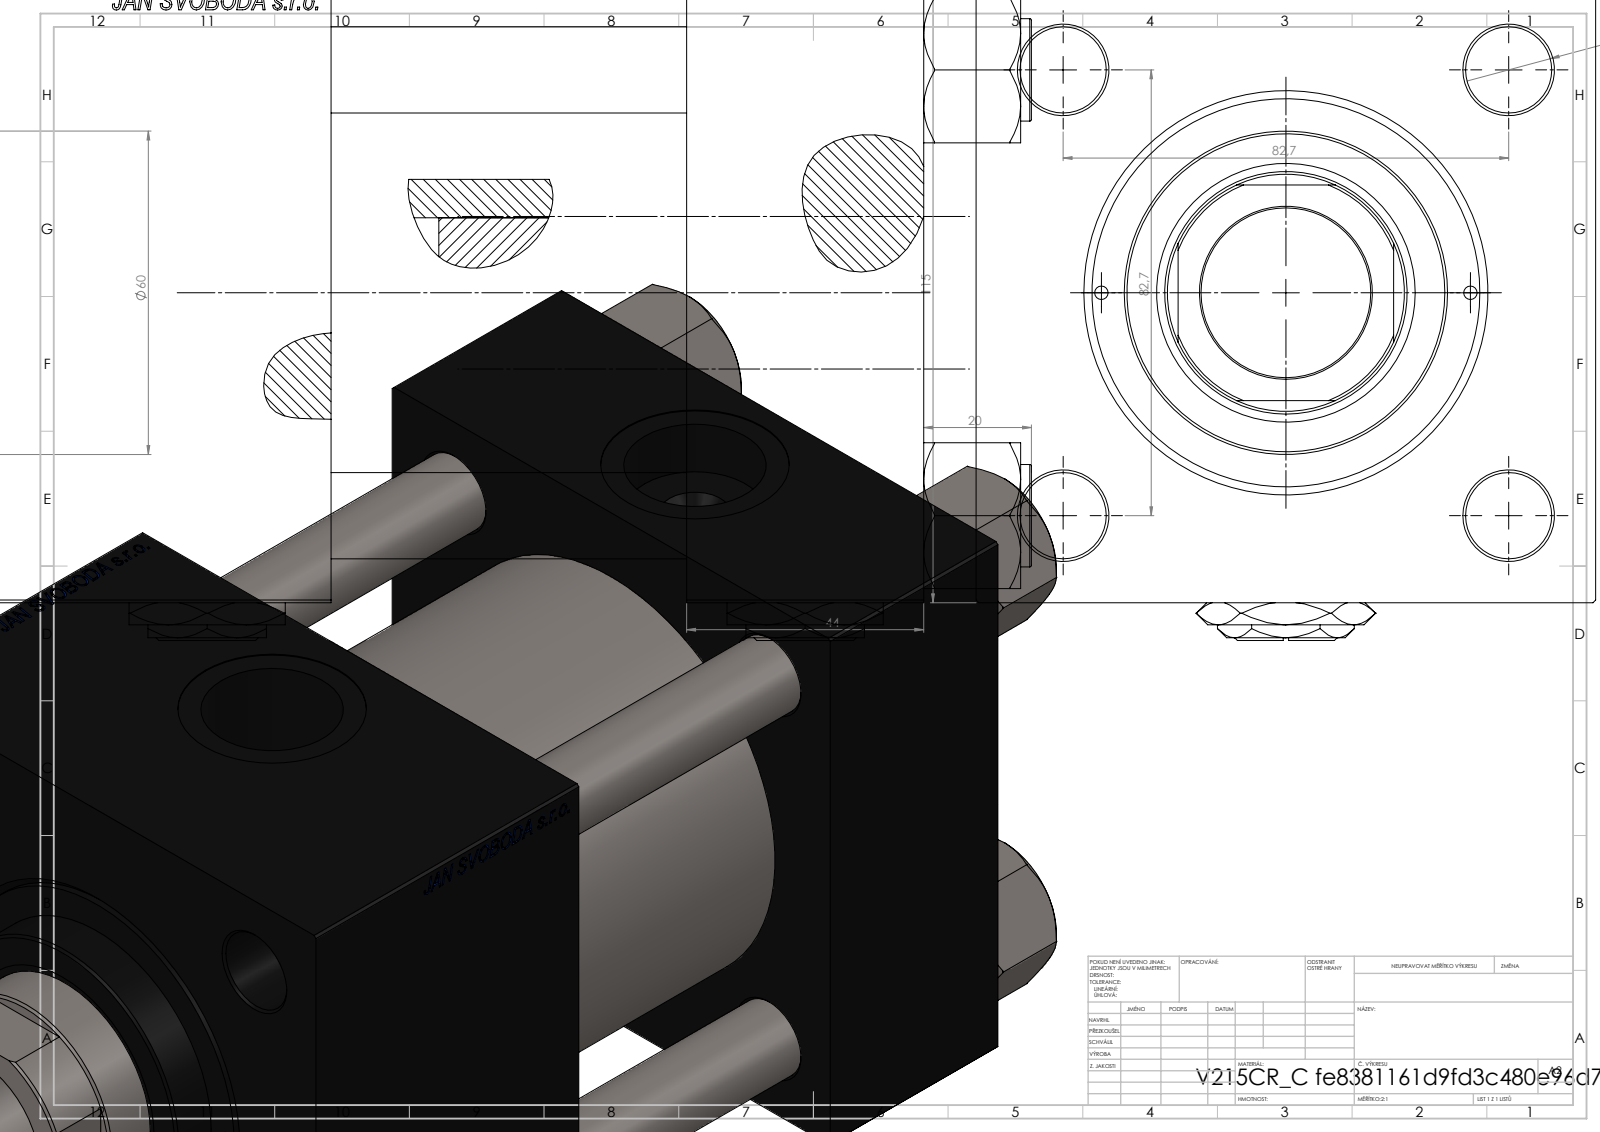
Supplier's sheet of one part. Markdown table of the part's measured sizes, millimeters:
| quantity | value |
| --- | --- |
| part name | V215CR_C_TYCINKA; Zatka_pro_OIL_PORT; V215CR_C_Body; V215_VC_A (+2 more) |
| STEP written by | SolidWorks 2019 (CONFIG_CONTROL_DESIGN) |
| units | millimeters |
| bodies | 13 solids, 1303 faces (623 planar, 102 cylindrical, 578 other) |
| overall size | 230 × 122 × 115 |
| volume | 1 804 000 mm³ |
| surface area | 281 024 mm² |
| round holes (diameter × count) | 16 × 4, 2.5 × 2, 7 × 2, 26.44 × 2, 35 × 2, 31.5 × 1, 45 × 1, 48 × 1, 61 × 1, 72 × 1, 80 × 1 |
| round bosses / shafts (diameter × count) | 19 × 4, 86 × 1, 60 × 1 |
| partial cylindrical surfaces (radius × count) | 22 × 1 |
| main face-to-face distances | 115, 44, 110, 179, 135, 69, 66, 20, 150.3, 106.3 |
| hole center spacings | 41.96, 58.48, 82.7, 86.17, 34.25, 116.96, 68.5, 111 |
